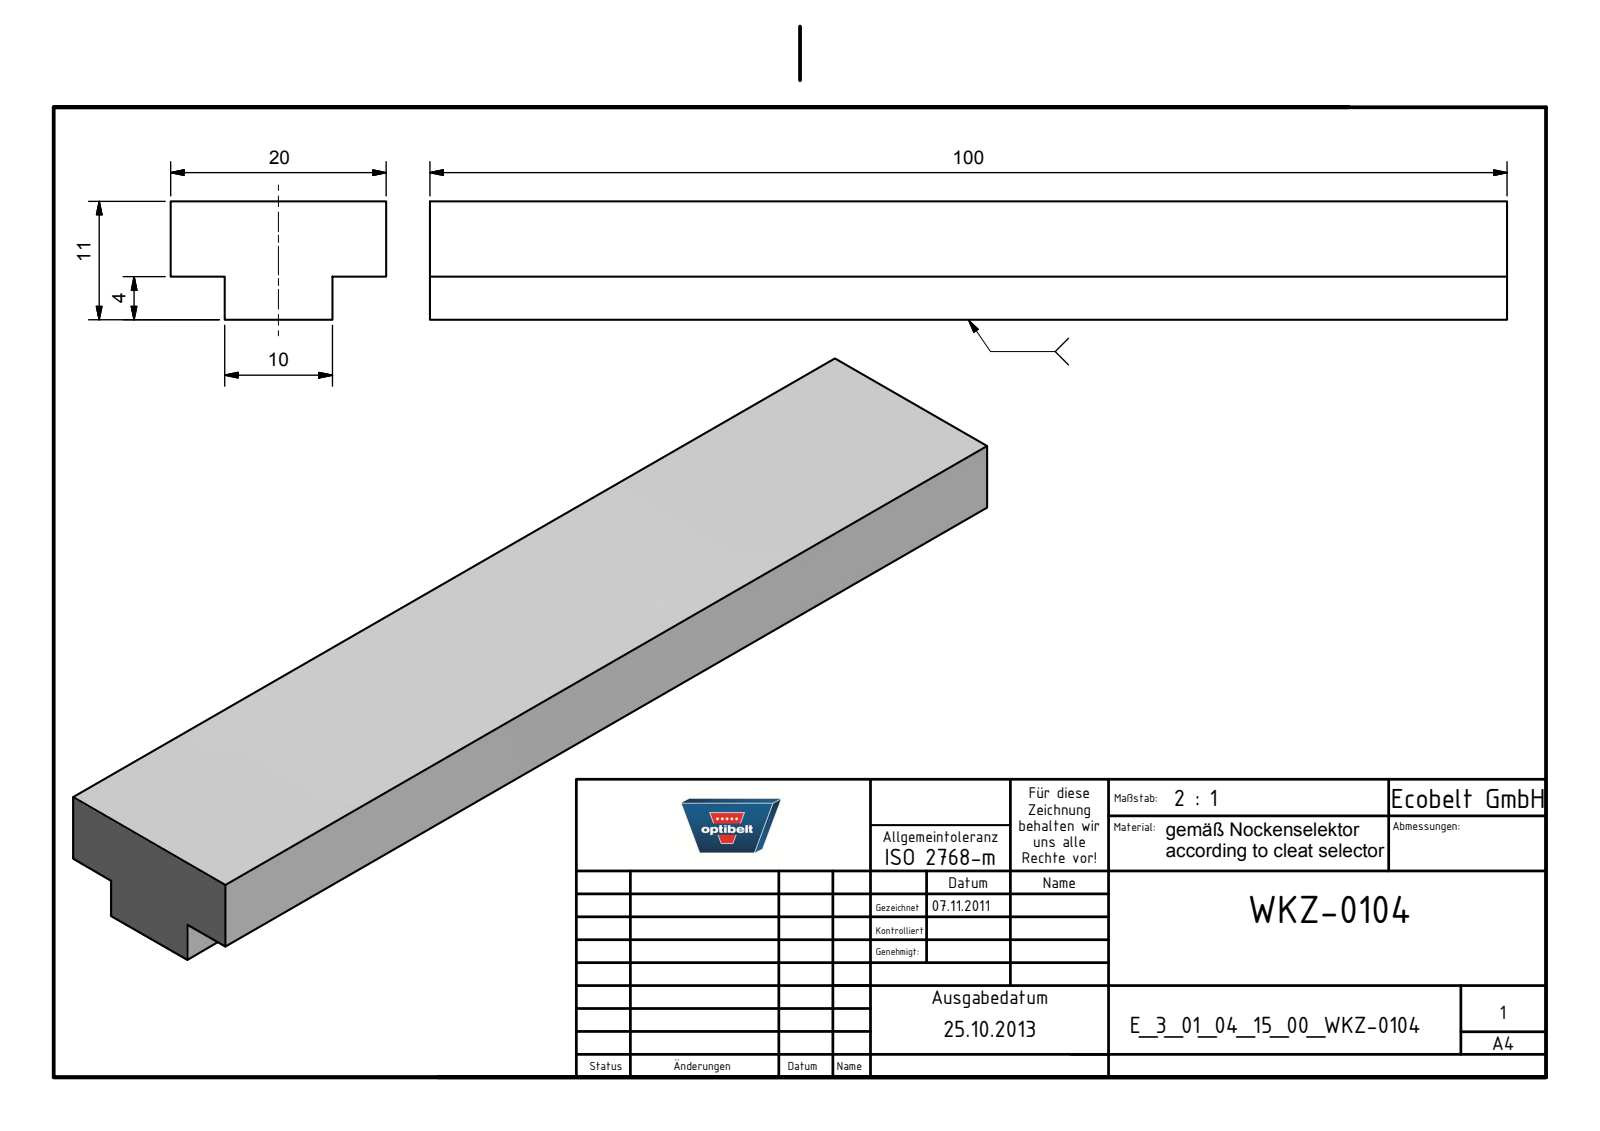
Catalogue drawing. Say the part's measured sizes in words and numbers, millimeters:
The part is named "E_3_01_04_15_00_WKZ-0104". Its 3-D file was written by "Autodesk Inventor 2025 (AUTOMOTIVE_DESIGN)". It is 1 solid with 10 faces: 10 planar, 0 cylindrical and 0 other. Overall it measures 100 by 20 by 11 millimeters. Its volume is 18 000 cubic millimeters and its surface area 6 560 square millimeters. The main face-to-face distances are 4, 11, 7, 5, 15, 20, 10, 100.
